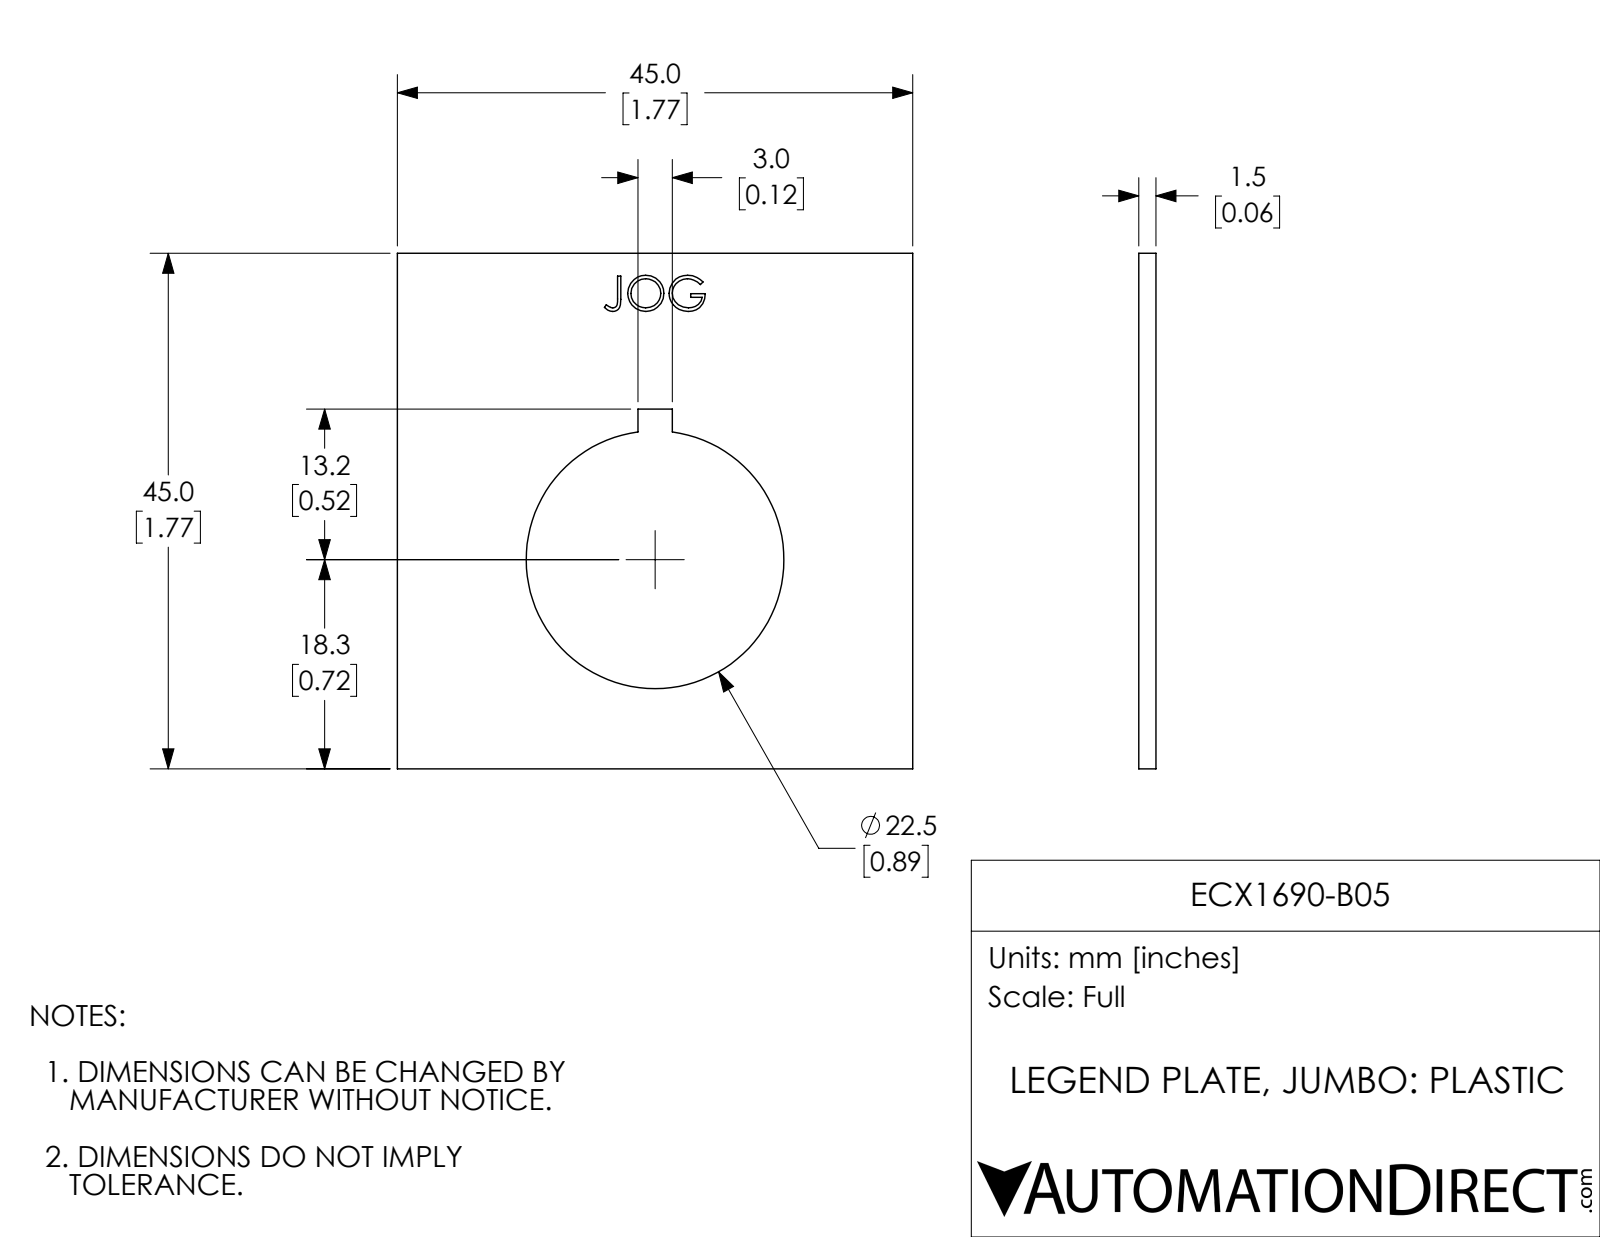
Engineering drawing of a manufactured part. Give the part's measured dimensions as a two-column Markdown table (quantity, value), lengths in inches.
| quantity | value |
| --- | --- |
| part name | ECX1690-B05 |
| STEP written by | SolidWorks 2018 (AUTOMOTIVE_DESIGN) |
| units | inches |
| bodies | 1 solid, 46 faces (21 planar, 3 cylindrical, 22 other) |
| overall size | 1.772 × 1.772 × 0.059 |
| volume | 0.148 in³ |
| surface area | 5.621 in² |
| round holes (diameter × count) | 0.886 × 1 |
| main face-to-face distances | 0.059, 1.772, 0.058, 0.827, 0.945, 1.236, 0.535, 0.118, 0.768, 0.177 |
